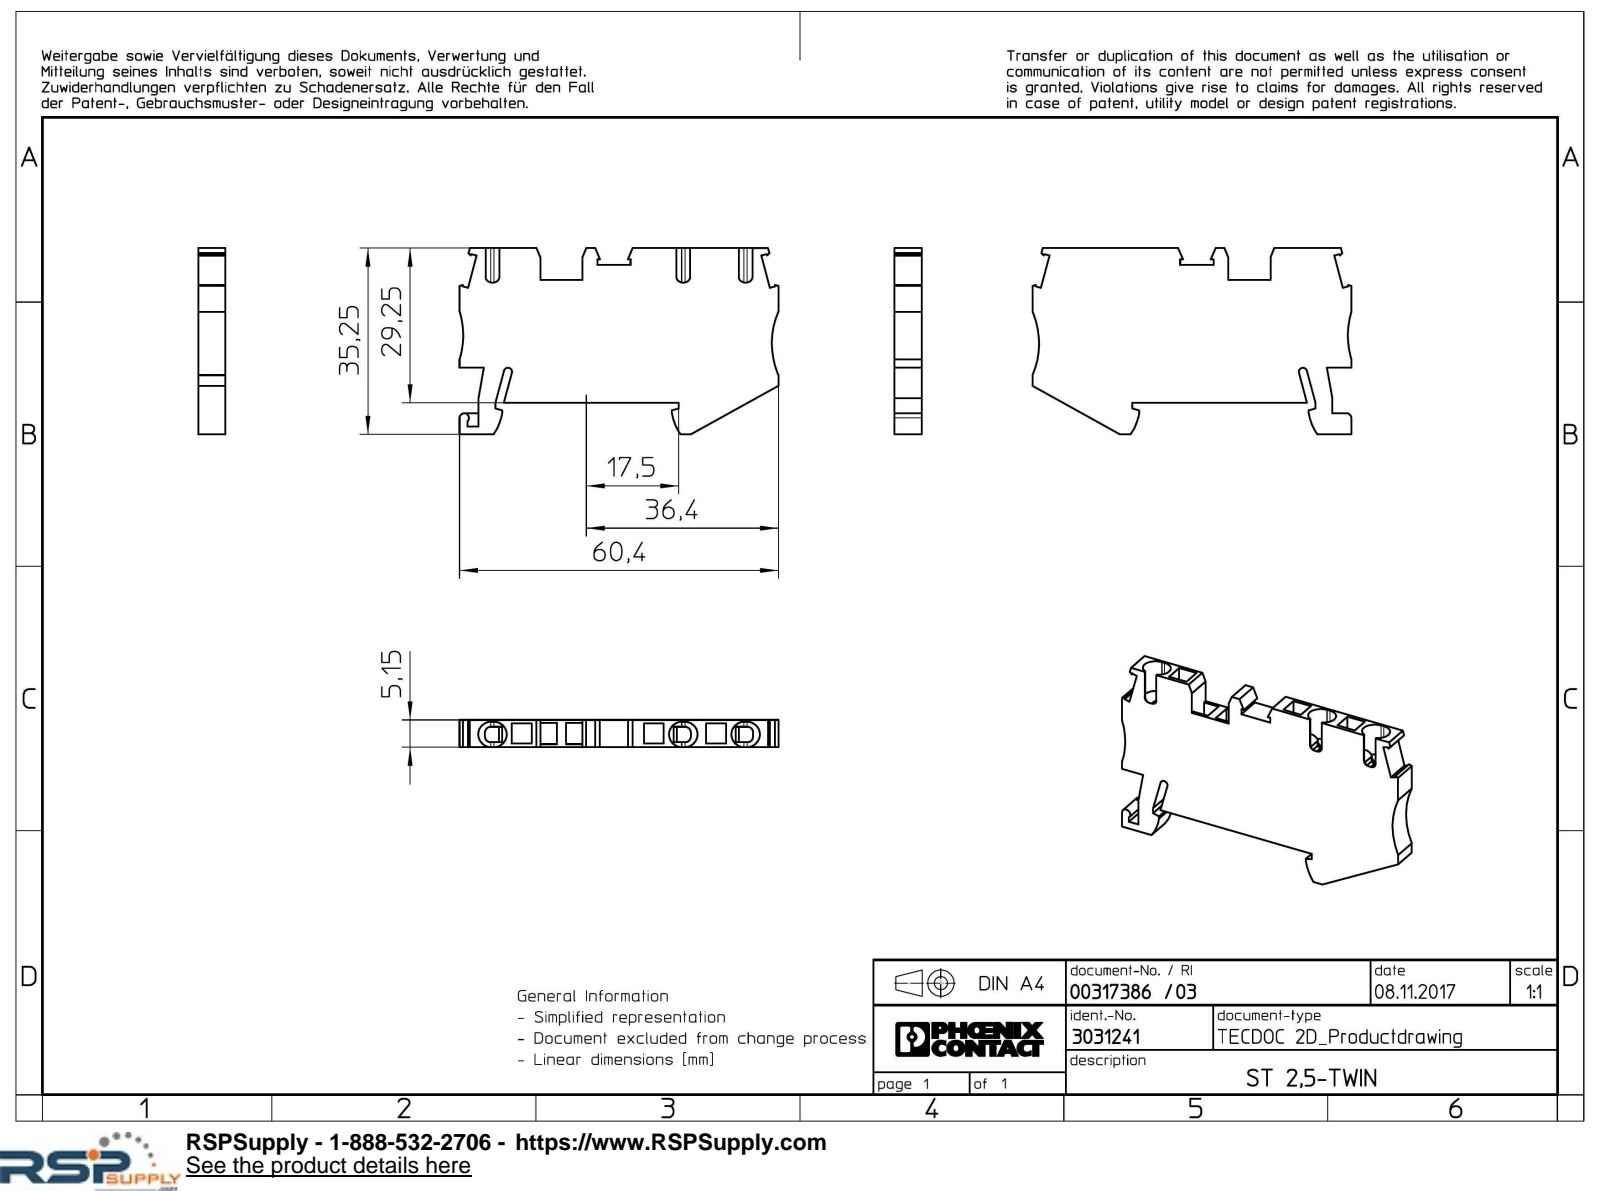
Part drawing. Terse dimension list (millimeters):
name: ST_2.5_TWIN-select
written by: Creo Elements/Direct Modeling 20.1A 29-Sep-2018 (C) Parametric Technology GmbH (AUTOMOTIVE_DESIGN)
unit: mm
bodies: 1 solid, 153 faces (119 planar, 25 cylindrical, 9 other)
size: 60.4 × 35.25 × 5.15
volume: 7 460 mm³; area: 5 794 mm²
rounds: 12× R1, 6× R2.4, 2× R9.5, 2× R15, 1× R0.7, 1× R0.8, 1× R0.9
face distances: 5.15, 3.15, 3.8, 0.65, 29.25, 4.85, 4.45, 8, 4, 3.85
